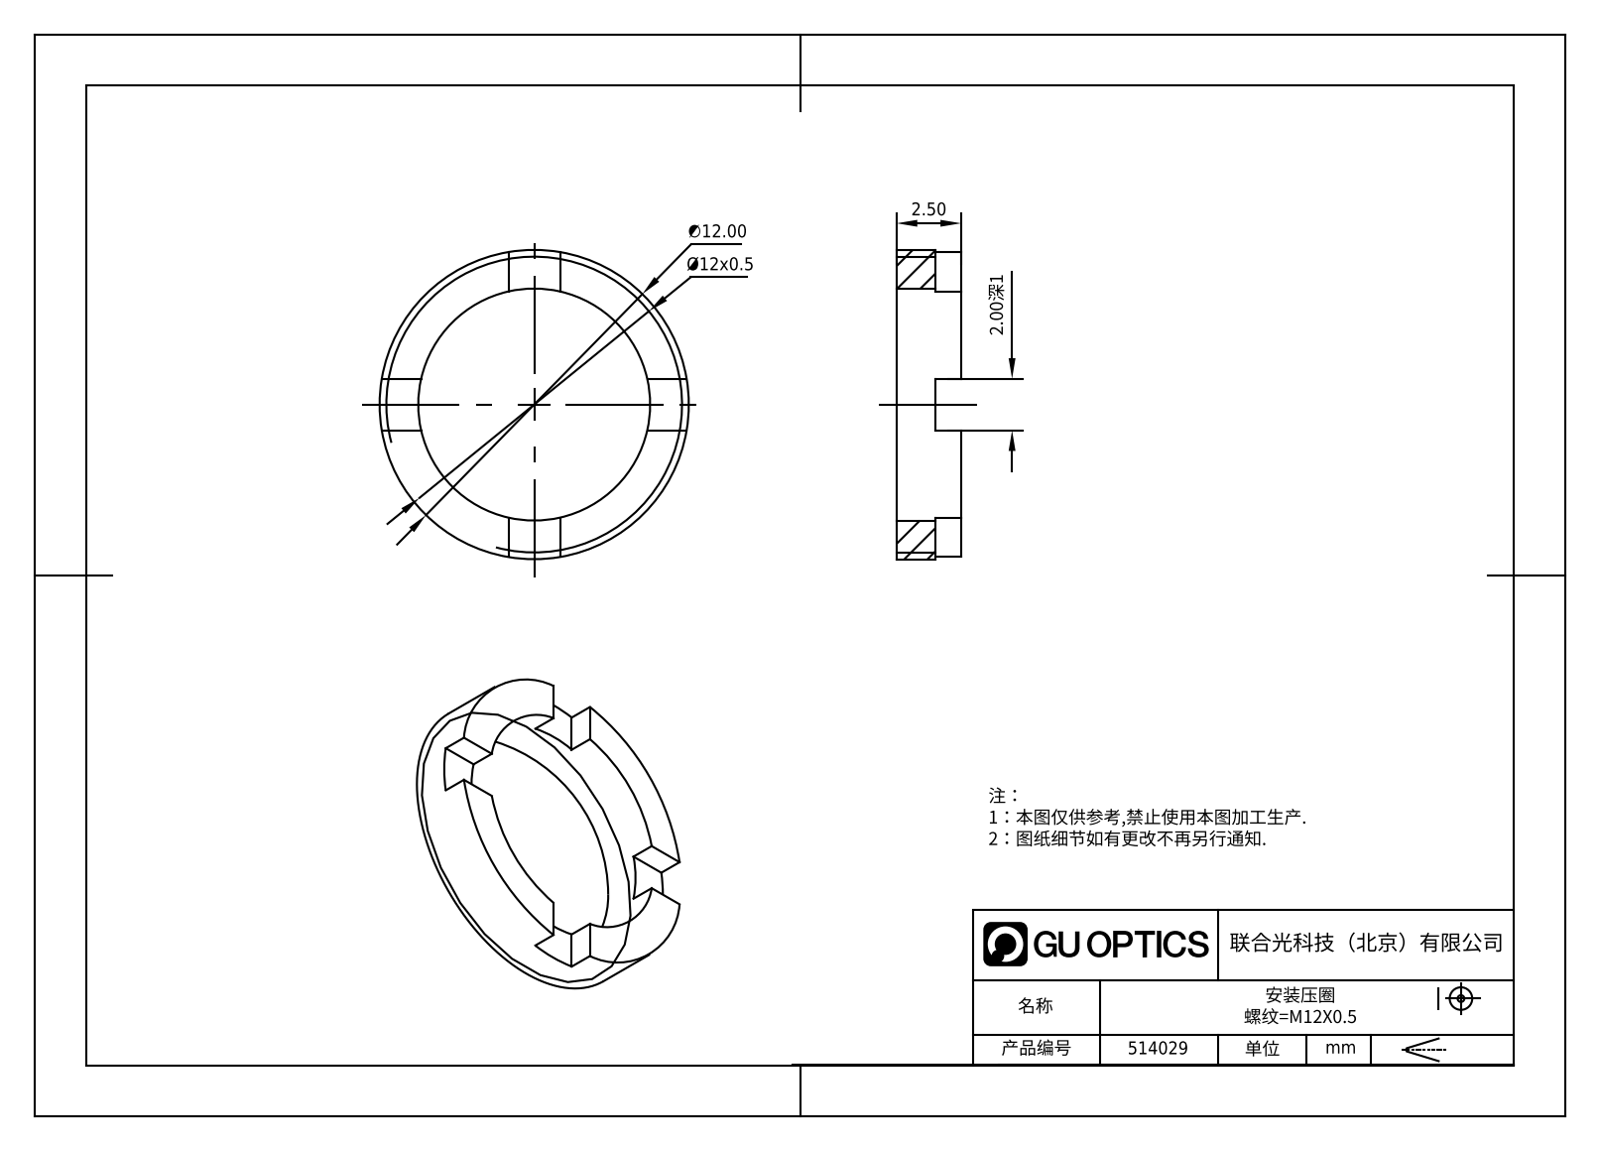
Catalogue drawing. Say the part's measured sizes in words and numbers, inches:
The part is named "514029". Its 3-D file was written by "SolidWorks 2020 (CONFIG_CONTROL_DESIGN)". It is 1 solid with 21 faces: 17 planar, 4 cylindrical and 0 other. Overall it measures 0.472 by 0.472 by 0.098 inches. Its volume is 0.007 cubic inches and its surface area 0.403 square inches. Round holes: 1 of diameter 0.354. Round bosses or shafts: 1 of diameter 0.472. The main face-to-face distances are 0.098, 0.059, 0.039, 0.079.
